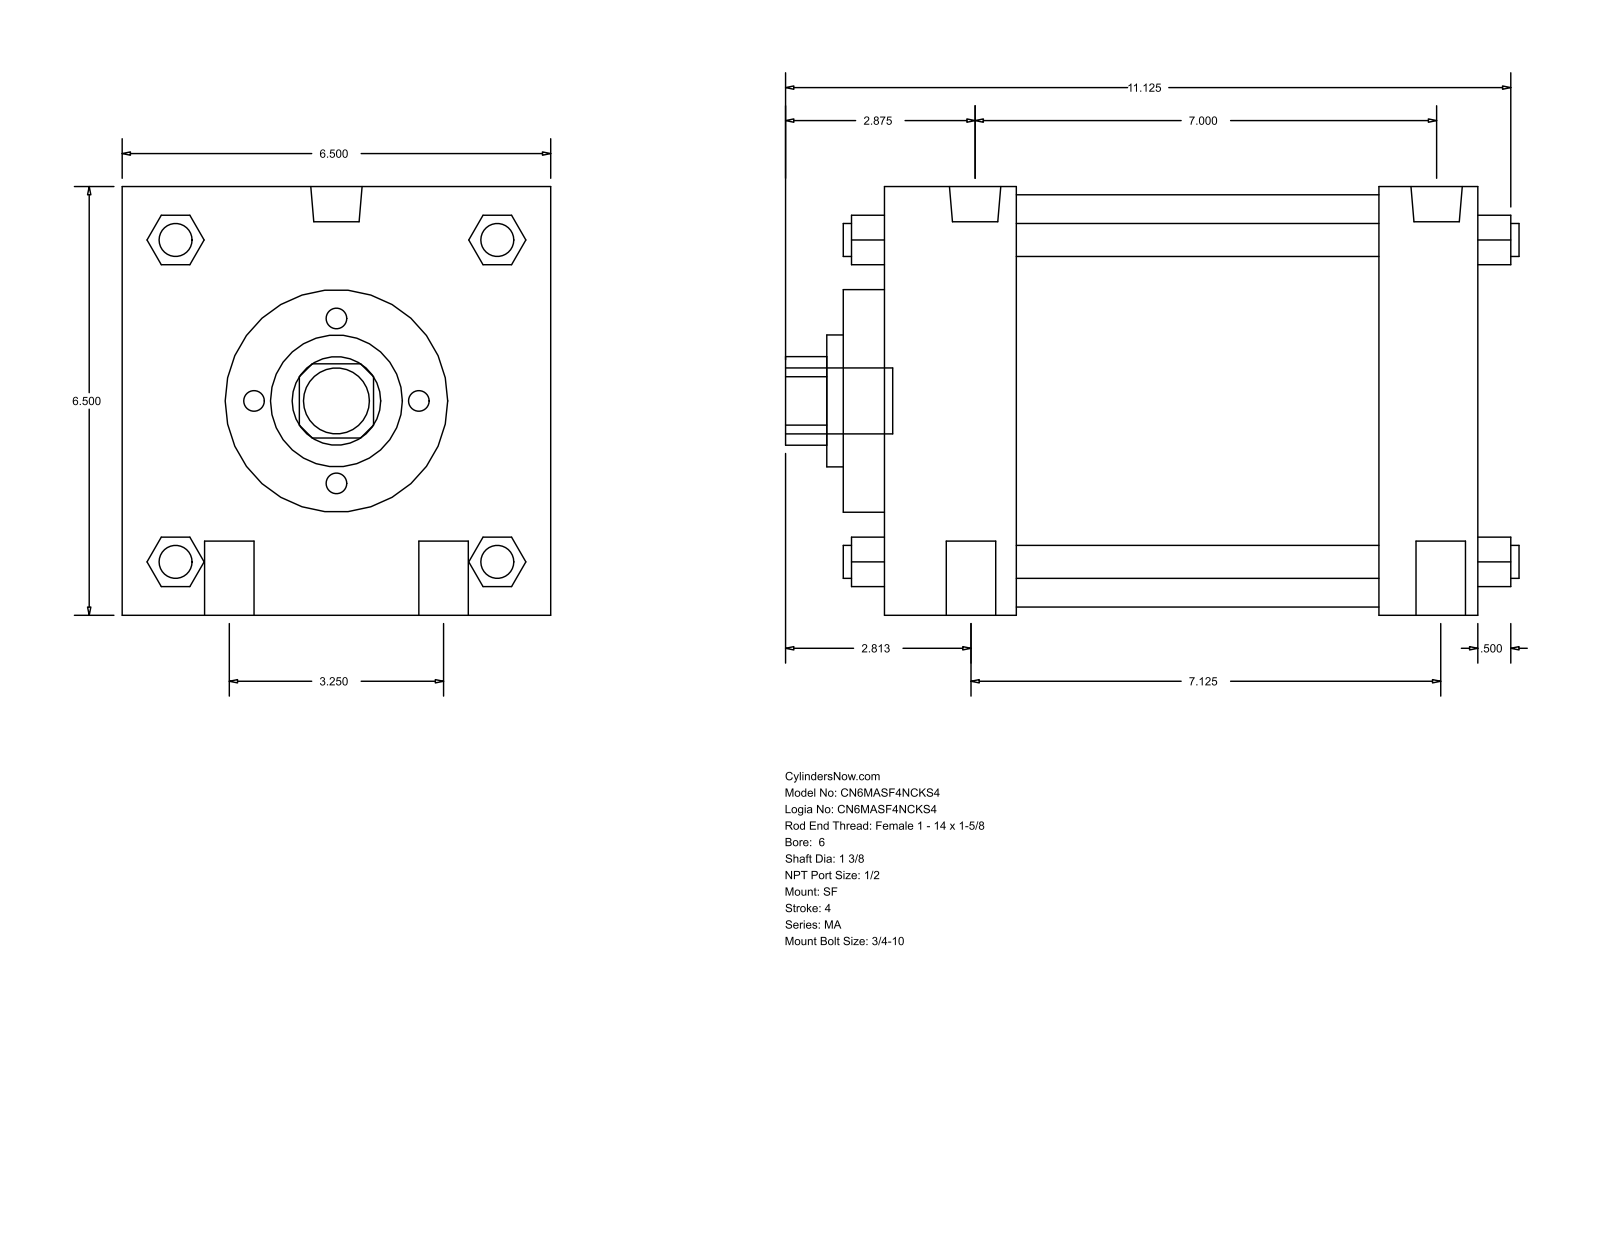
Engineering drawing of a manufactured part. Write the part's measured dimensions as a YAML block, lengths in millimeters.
part_name: "MA_SF__0600_1.375"
step_written_by: "GSSL Pune (CONFIG_CONTROL_DESIGN)"
units: millimeters
bodies: {solids: 0, faces: 126, planar: 95, cylindrical: 31, other: 0}
overall_size: [282.57, 165.1, 165.1]
round_holes:
  - {diameter: 34.92, count: 1}
  - {diameter: 50.8, count: 1}
  - {diameter: 85.72, count: 1}
  - {diameter: 158.75, count: 1}
round_bosses_or_shafts:
  - {diameter: 19.05, count: 4}
  - {diameter: 12.7, count: 4}
  - {diameter: 19.77, count: 2}
  - {diameter: 17.46, count: 2}
  - {diameter: 25.4, count: 1}
partial_cylinders:
  - {radius: 17.06, count: 1}
face_to_face_distances: [165.1, 228.6, 190.5, 50.8, 38.1, 139.7, 177.8, 15.87, 244.47, 66.67]
